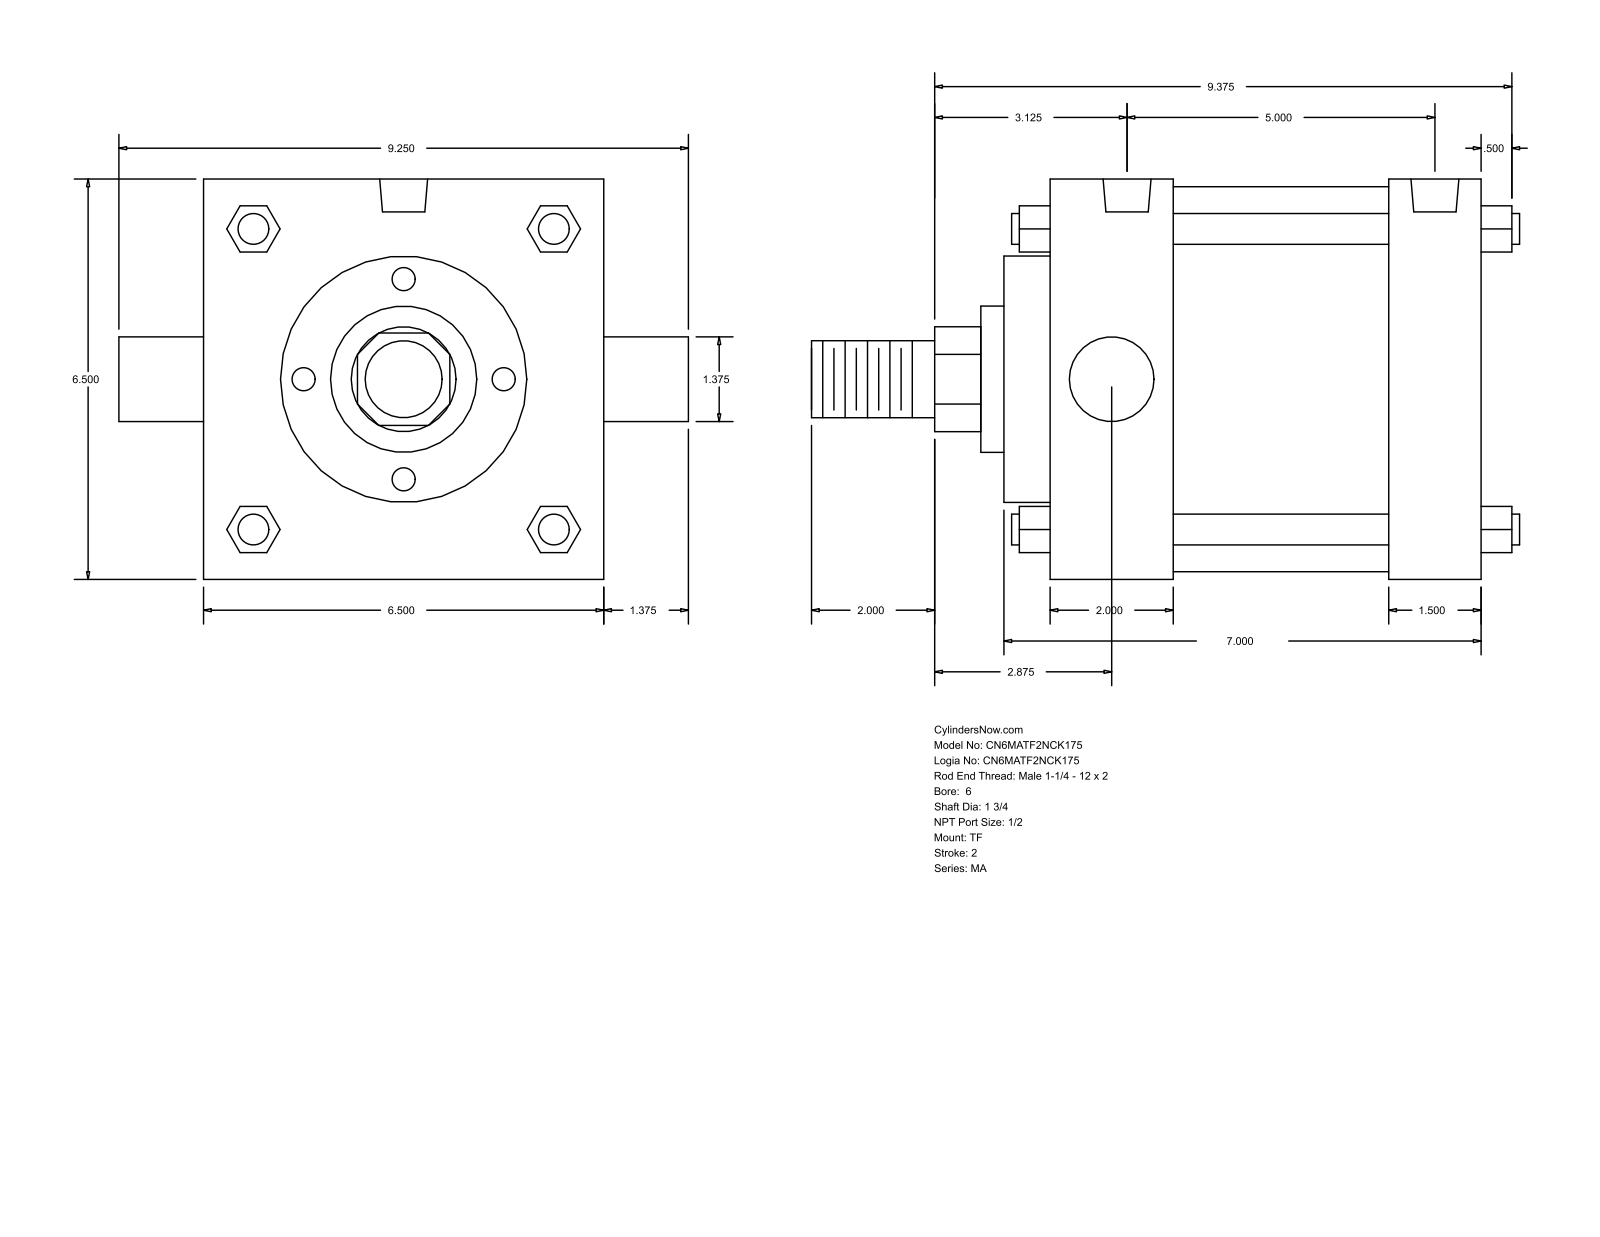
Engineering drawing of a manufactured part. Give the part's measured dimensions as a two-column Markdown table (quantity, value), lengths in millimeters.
| quantity | value |
| --- | --- |
| part name | MA_TF__0600_1.75 |
| STEP written by | GSSL Pune (CONFIG_CONTROL_DESIGN) |
| units | millimeters |
| bodies | 0 solids, 122 faces (93 planar, 29 cylindrical, 0 other) |
| overall size | 292.1 × 234.95 × 165.1 |
| round holes (diameter × count) | 17.46 × 3, 19.77 × 2 |
| round bosses / shafts (diameter × count) | 12.7 × 4, 158.75 × 1, 101.6 × 1, 60.33 × 1, 44.45 × 1, 34.92 × 1, 31.75 × 1 |
| partial cylindrical surfaces (radius × count) | 21.63 × 1 |
| main face-to-face distances | 165.1, 177.81, 19.05, 50.8, 139.7, 127.01, 88.9, 38.11, 69.85, 158.75 |
| hole center spacings | 127 |
